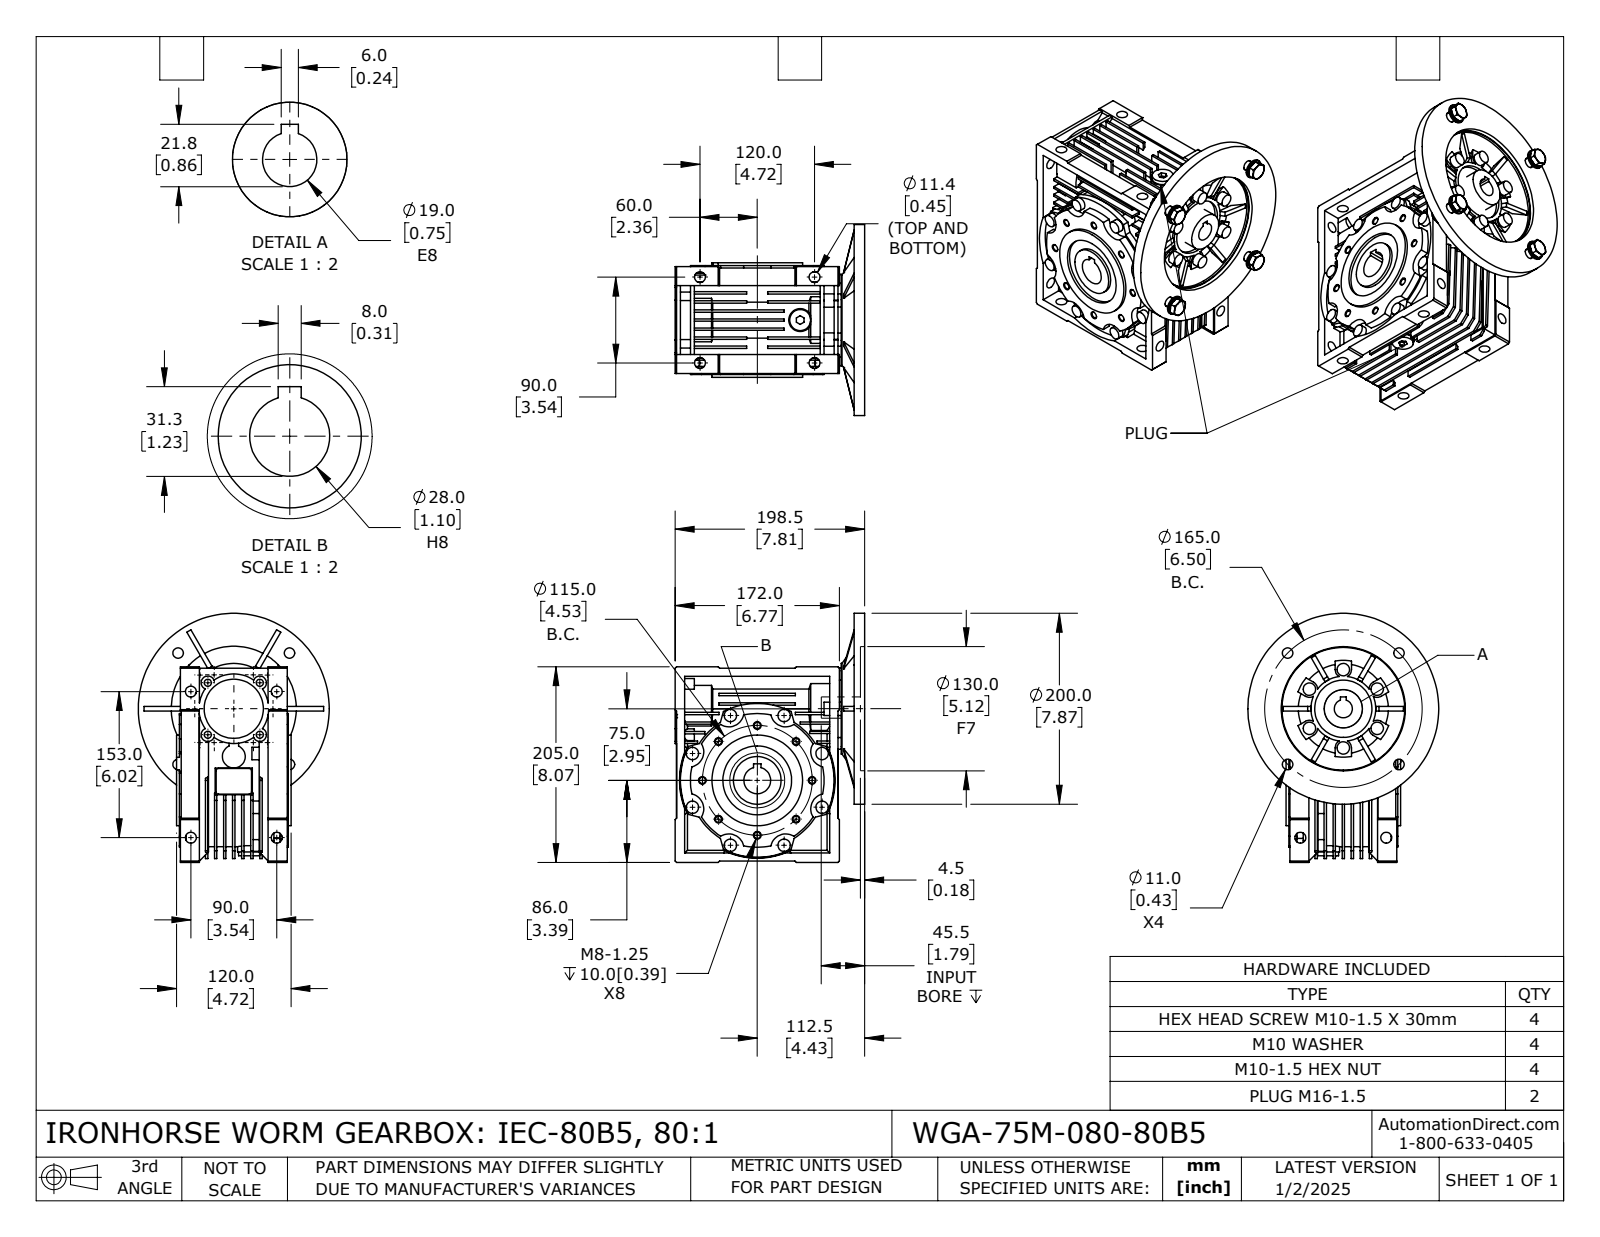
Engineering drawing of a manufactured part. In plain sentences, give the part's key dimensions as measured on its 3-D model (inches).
The part is named "WGA-75M-080-80B5". Its 3-D file was written by "SolidWorks 2024 (CONFIG_CONTROL_DESIGN)". It is 20 solids with 1447 faces: 790 planar, 439 cylindrical and 218 other. Overall it measures 10.276 by 8.462 by 7.874 inches. Its volume is 186.2 cubic inches and its surface area 831.4 square inches. Round holes: 8 of diameter 0.262, 8 of diameter 0.448, 4 of diameter 0.293, 4 of diameter 0.335, 4 of diameter 0.394, 4 of diameter 0.413, 4 of diameter 0.433, 2 of diameter 0.571, 1 of diameter 0.748, 1 of diameter 0.787, 1 of diameter 1.102, 1 of diameter 1.535. Round bosses or shafts: 14 of diameter 0.512, 4 of diameter 0.787, 4 of diameter 0.63, 3 of diameter 0.945, 2 of diameter 3.74, 2 of diameter 0.866, 2 of diameter 0.622, 2 of diameter 0.539. Partial cylindrical surfaces (rounded edges, fillets, slot ends): 10 of radius 0.276, 8 of radius 0.63, 6 of radius 0.335, 4 of radius 0.098, 1 of radius 1.338, 1 of radius 1.417, 1 of radius 1.437, 1 of radius 1.535. The main face-to-face distances are 0.374, 0.098, 0.748, 0.472, 0.276, 1.122, 0.65, 0.394, 1.093, 0.846. The hole center spacings are 1.733, 2.264, 3.202, 3.584, 4.183, 1.515, 2.143, 3.248.
